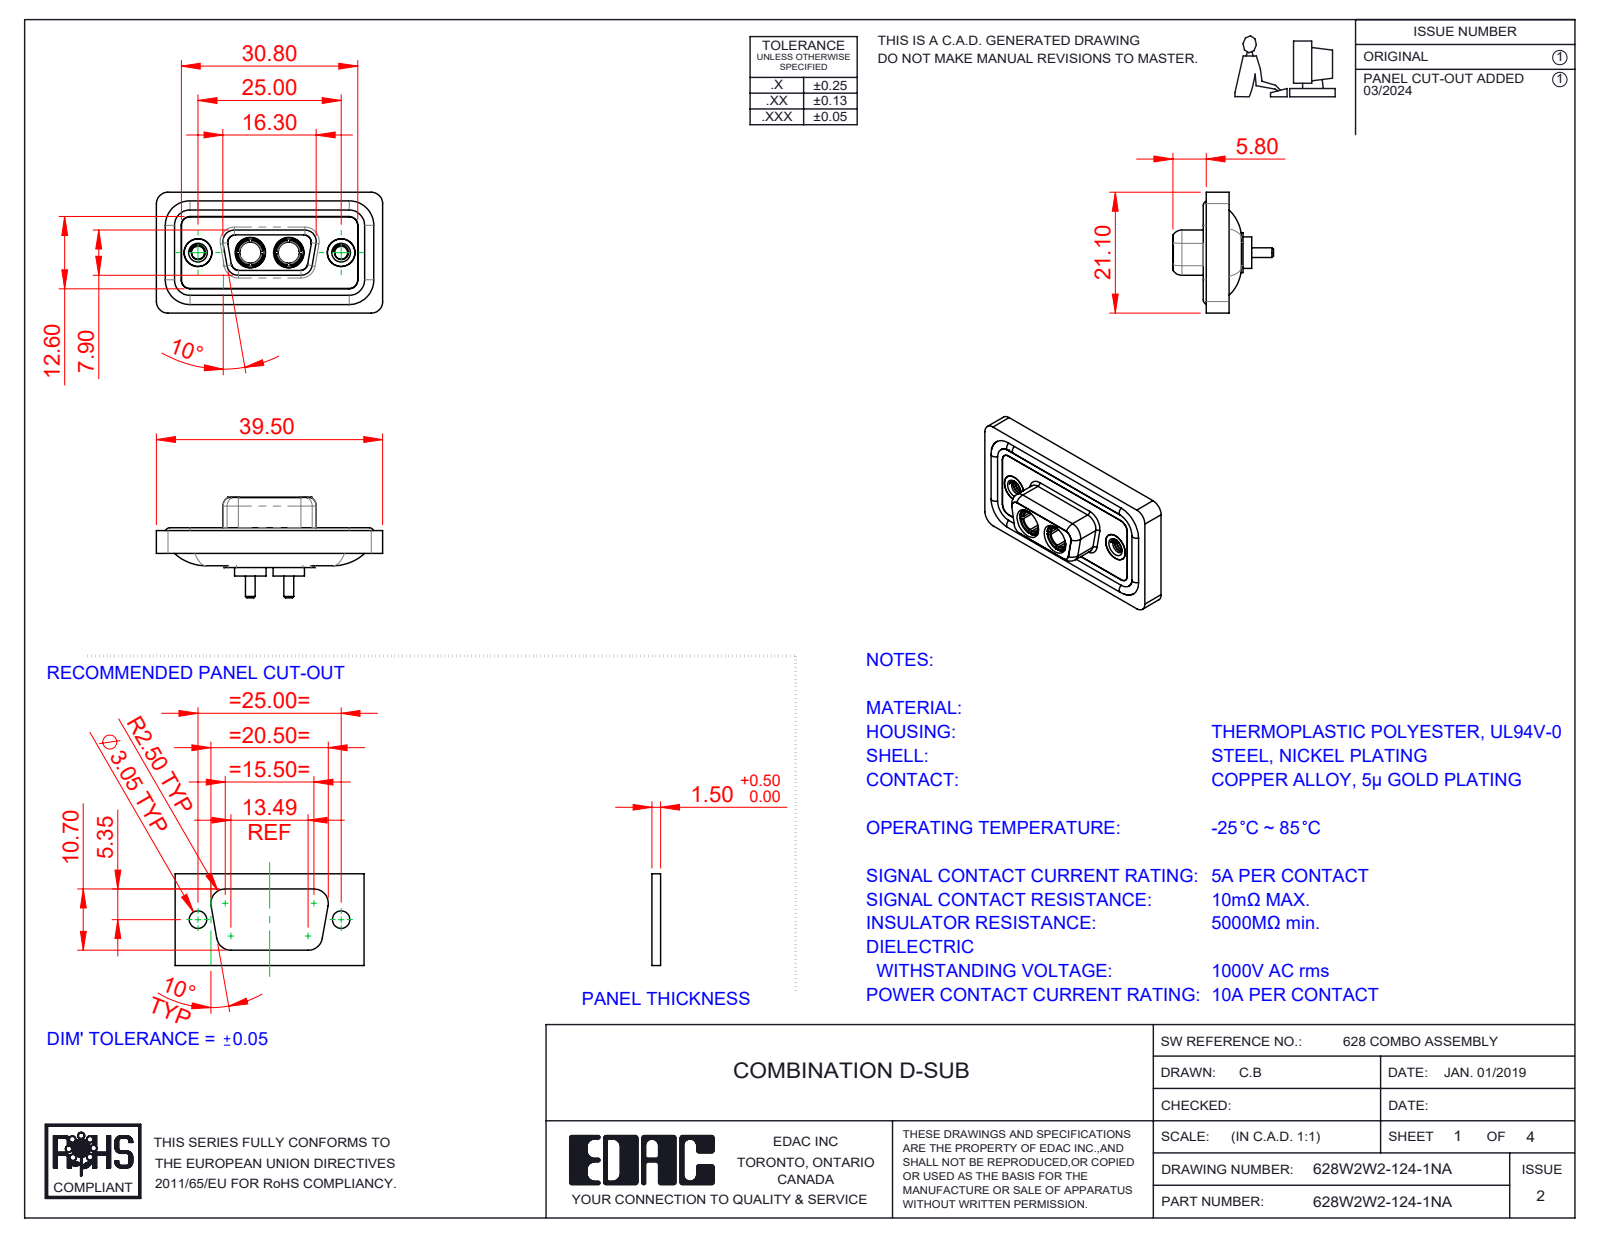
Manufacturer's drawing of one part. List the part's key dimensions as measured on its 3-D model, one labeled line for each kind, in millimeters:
Part name (STEP PRODUCT): 628Combo Shell Rear_09 Contacts; 628Combo Shell Front_09 Contacts; 628Combo Housing_2W2; 628Combo Threaded Rivet_A (+3 more)
STEP written by: SolidWorks 2023 (CONFIG_CONTROL_DESIGN)
Units: millimetres
Bodies: 11 solids, 532 faces (163 planar, 236 cylindrical, 133 other)
Overall size (bounding box): 39.5 × 21.1 × 17.55
Volume: 4 685 mm³ · Surface area: 7 608 mm²
Round holes (diameter × count): ⌀4.85 ×4, ⌀2.26 ×2, ⌀3.7 ×2, ⌀4 ×2, ⌀4.05 ×2, ⌀5 ×2, ⌀5.3 ×2
Round bosses / shafts (diameter × count): ⌀1.6 ×4, ⌀5.5 ×2, ⌀5.2 ×2, ⌀4.96 ×2, ⌀4.95 ×2, ⌀4.8 ×2, ⌀4.75 ×2, ⌀3.75 ×2
Partial cylindrical surfaces — rounded edges, fillets, slot ends (radius × count): R1.5 ×22, R2 ×18, R1.35 ×8, R1.6 ×8, R0.25 ×4, R0.5 ×4, R0.6 ×4, R0.65 ×4
Main face-to-face distances: 0.4, 1.8, 1.1, 2.9, 0.5, 1.6, 5.65, 1.5, 7.45, 5.35
Hole centre spacings: 9.14, 15.86, 6.72, 25
